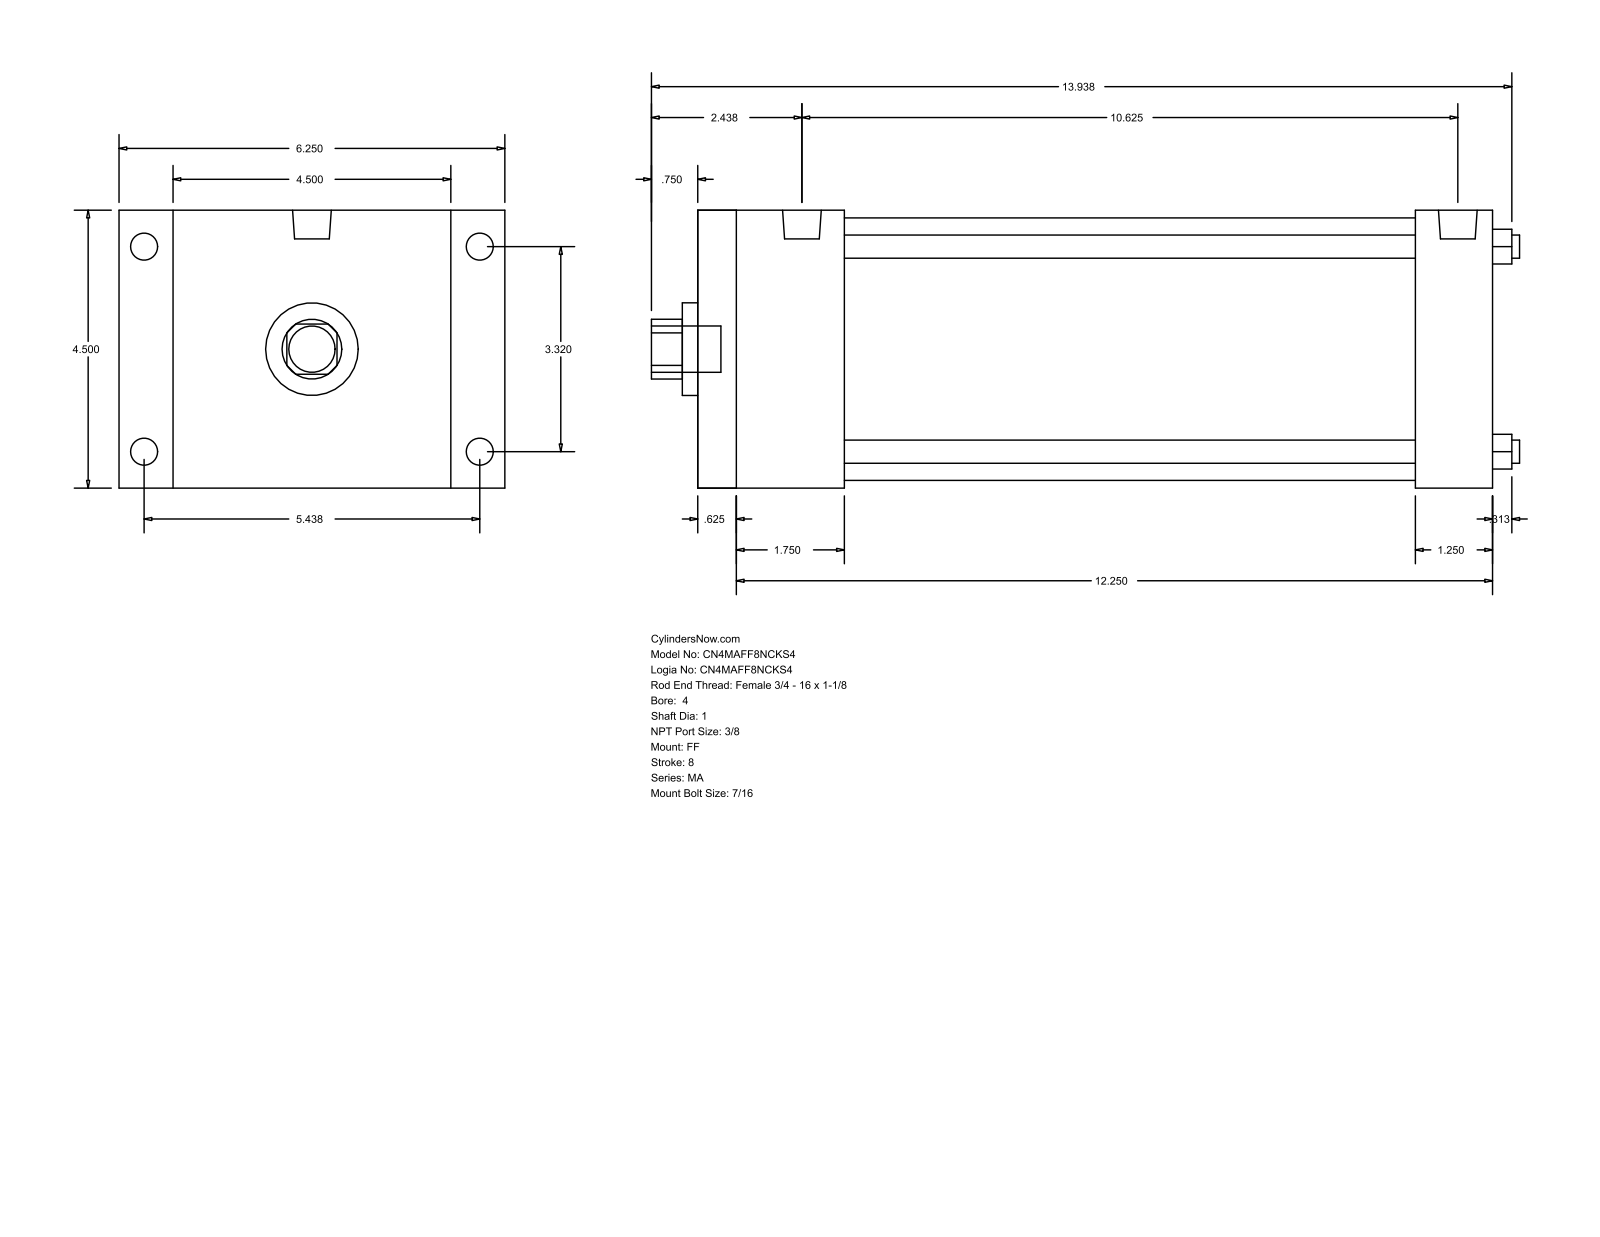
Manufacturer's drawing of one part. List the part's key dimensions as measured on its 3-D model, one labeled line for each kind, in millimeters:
Part name (STEP PRODUCT): MA_FF__0400_1
STEP written by: GSSL Pune (CONFIG_CONTROL_DESIGN)
Units: millimetres
Bodies: 0 solids, 92 faces (64 planar, 28 cylindrical, 0 other)
Overall size (bounding box): 357.19 × 158.75 × 114.3
Round holes (diameter × count): ⌀9.53 ×4, ⌀25.4 ×1, ⌀38.1 ×1, ⌀107.95 ×1
Round bosses / shafts (diameter × count): ⌀11.11 ×8, ⌀15.93 ×2, ⌀19.05 ×1
Partial cylindrical surfaces — rounded edges, fillets, slot ends (radius × count): R12.29 ×1
Main face-to-face distances: 114.3, 327.02, 15.87, 311.15, 22.23, 136.53, 295.27, 279.4, 31.75, 60.33
Hole centre spacings: 59.62, 84.32, 119.25
